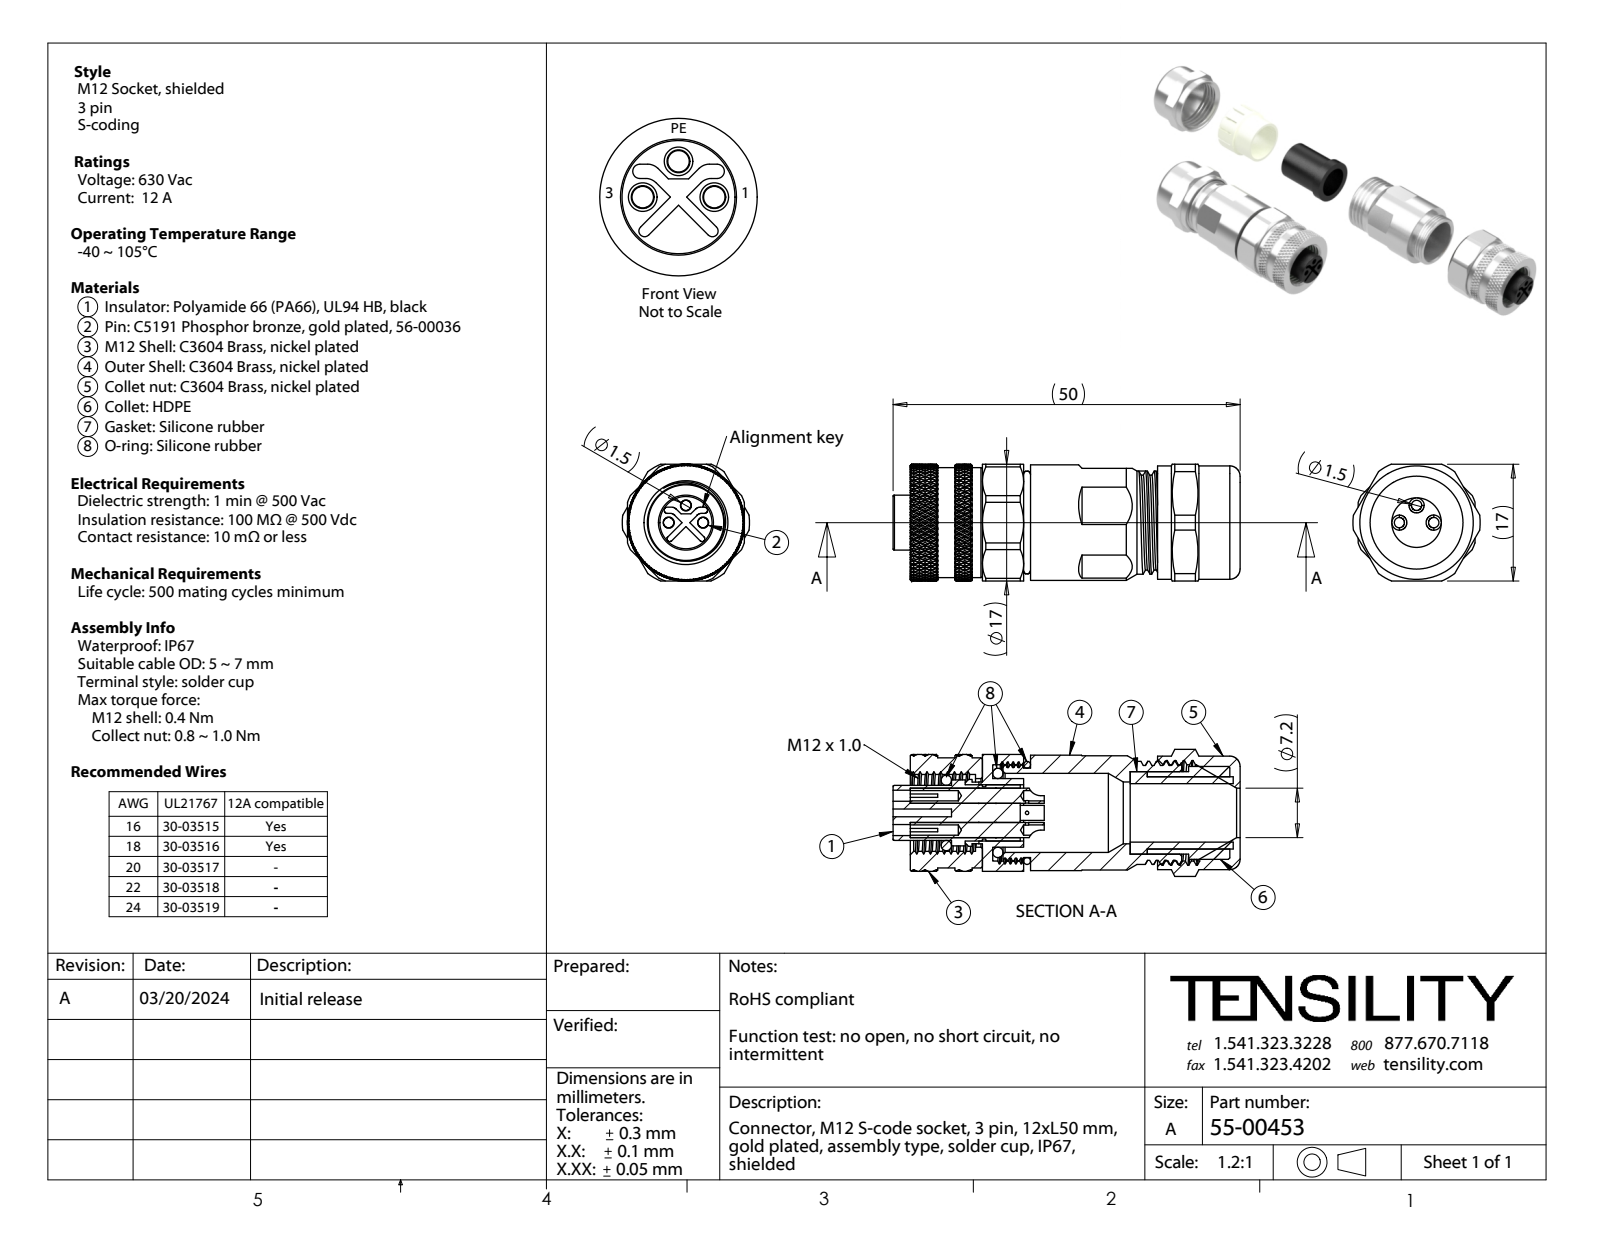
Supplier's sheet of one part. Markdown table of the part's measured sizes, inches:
| quantity | value |
| --- | --- |
| part name | 55-00453-08; 55-00453-07; 55-00453-04; 55-00453-03 (+8 more) |
| STEP written by | SolidWorks 2021 (CONFIG_CONTROL_DESIGN) |
| units | inches |
| bodies | 13 solids, 501 faces (182 planar, 191 cylindrical, 128 other) |
| overall size | 1.988 × 0.728 × 0.669 |
| volume | 0.453 in³ |
| surface area | 17.6 in² |
| round holes (diameter × count) | 0.059 × 3, 0.063 × 3, 0.02 × 2, 0.283 × 1, 0.299 × 1, 0.323 × 1, 0.335 × 1, 0.354 × 1, 0.394 × 1, 0.413 × 1, 0.441 × 1, 0.453 × 1 |
| round bosses / shafts (diameter × count) | 0.087 × 3, 0.669 × 1, 0.661 × 1, 0.65 × 1, 0.63 × 1, 0.591 × 1, 0.531 × 1, 0.512 × 1 |
| partial cylindrical surfaces (radius × count) | 0.039 × 4, 0.073 × 3, 0.016 × 2, 0.018 × 2, 0.354 × 1, 0.364 × 1 |
| main face-to-face distances | 0.669, 0.059, 0.236, 0.63, 0.039, 0.413, 1.201, 1.358, 0.276, 0.177 |
| hole center spacings | 0.098, 0.139, 0.197 |
